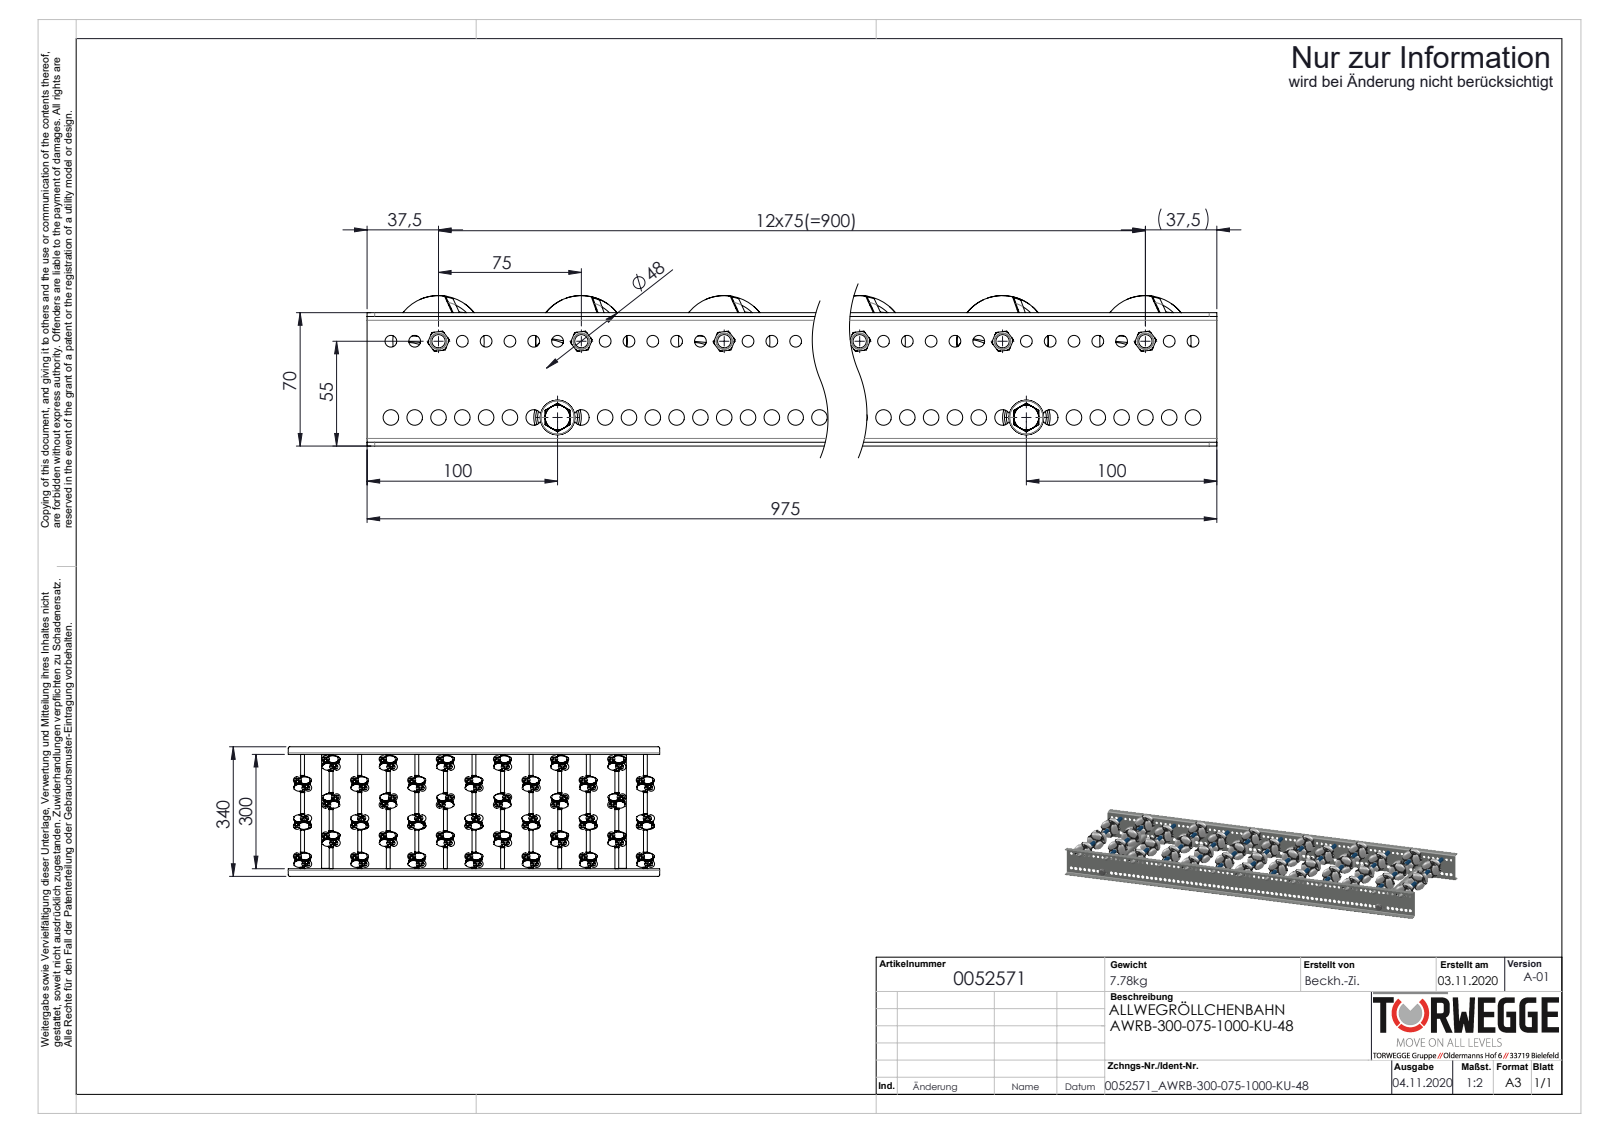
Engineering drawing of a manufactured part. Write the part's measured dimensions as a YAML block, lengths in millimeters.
part_name: "Profil-RB-20x70x20x2_S100234_U-PROFIL-20-70-20-2-RB-L=975; 0036819_SICHERUNGS-HUTMUTTER-DIN986-M6; AWR48_Halter; AWR-Achse-für-Konfiguration_L300 (+8 more)"
step_written_by: "SolidWorks 2020 (AUTOMOTIVE_DESIGN)"
units: millimeters
bodies: {solids: 675, faces: 12362, planar: 4176, cylindrical: 4858, other: 3328}
overall_size: [975, 340, 78.99]
volume: 2375000
surface_area: 1687000
round_holes:
  - {diameter: 3.7, count: 234}
  - {diameter: 4.2, count: 234}
  - {diameter: 6.2, count: 77}
  - {diameter: 8.2, count: 77}
  - {diameter: 4.92, count: 13}
  - {diameter: 6.5, count: 13}
  - {diameter: 8.4, count: 13}
  - {diameter: 6.8, count: 2}
  - {diameter: 21, count: 2}
round_bosses_or_shafts:
  - {diameter: 4, count: 234}
  - {diameter: 3.7, count: 201}
  - {diameter: 8, count: 15}
  - {diameter: 42, count: 13}
  - {diameter: 11, count: 13}
  - {diameter: 10, count: 13}
  - {diameter: 7, count: 13}
  - {diameter: 6, count: 13}
partial_cylinders:
  - {radius: 23.55, count: 13}
  - {radius: 4, count: 8}
  - {radius: 2, count: 4}
face_to_face_distances: [2, 302, 68, 300, 304, 66, 70, 3, 20, 5]
hole_center_spacings: [36.06, 36.05, 75, 36.07, 150, 36.04, 49.63, 125.34]
